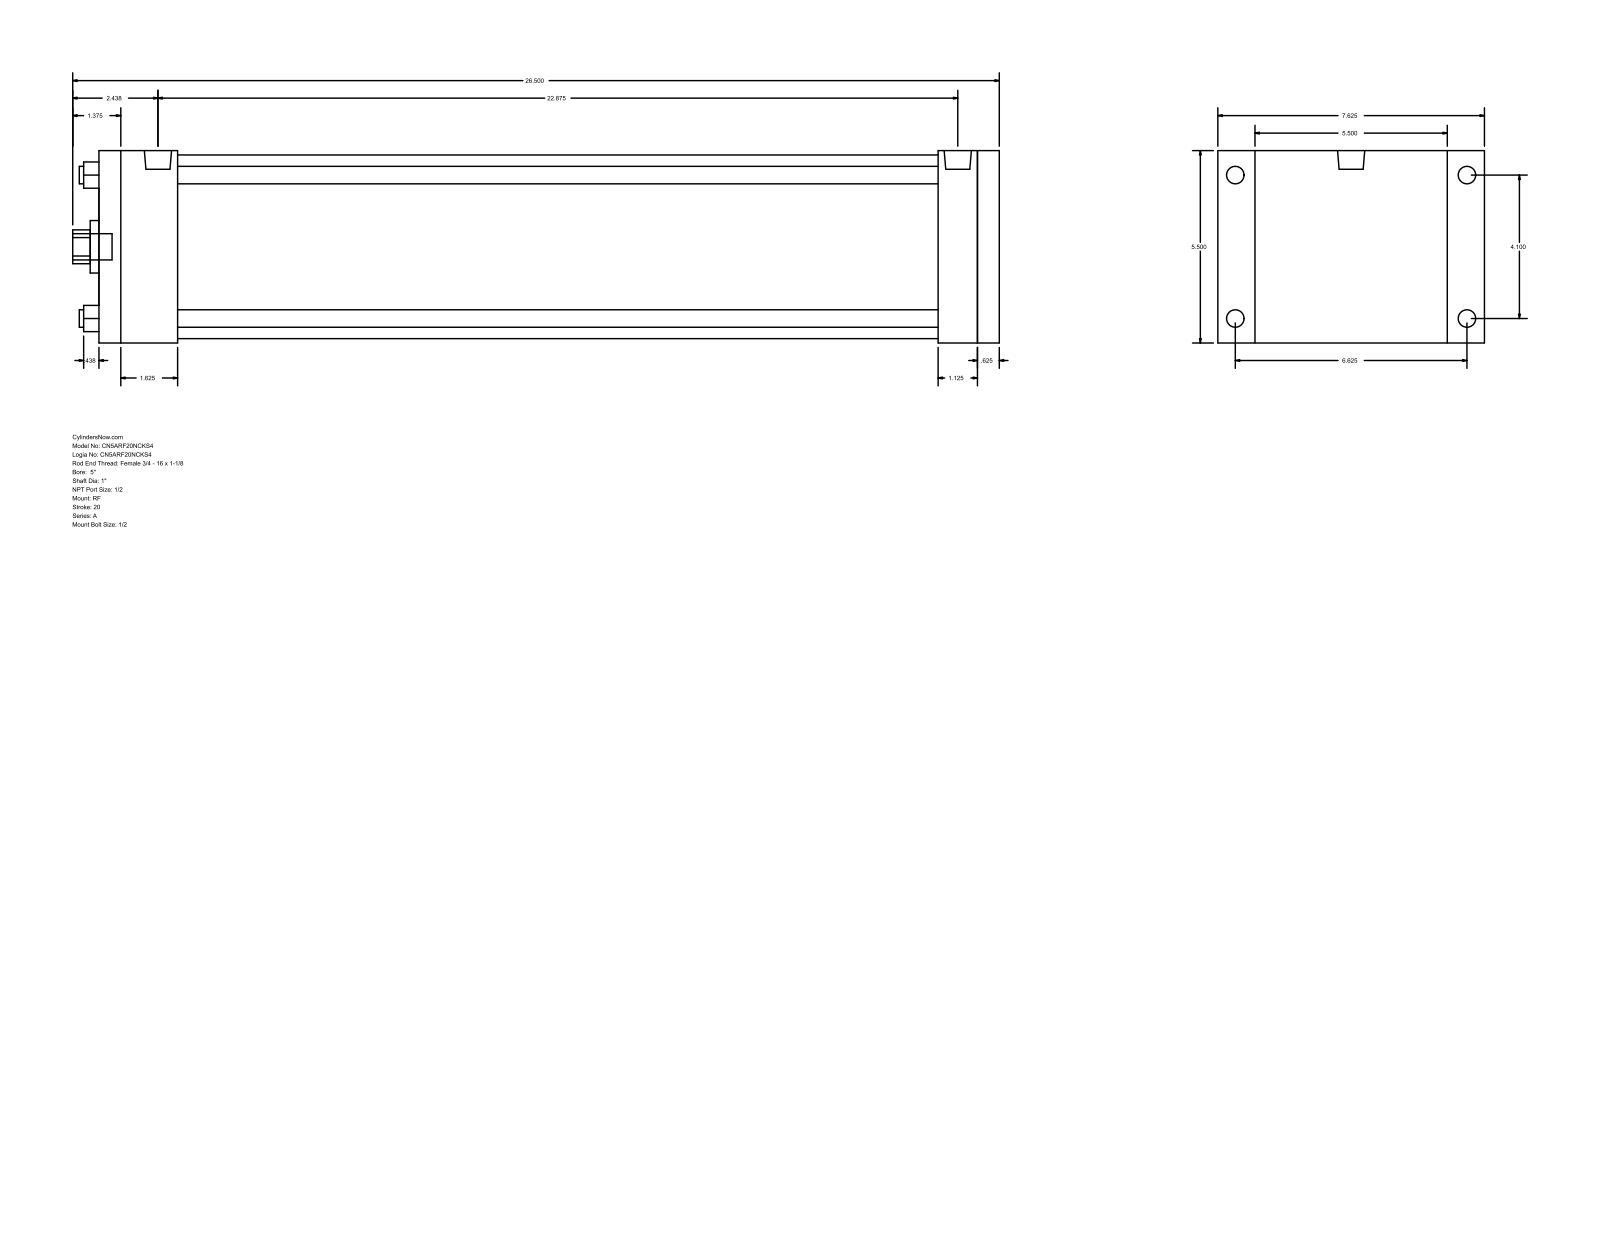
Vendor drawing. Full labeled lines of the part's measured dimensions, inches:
Part name (STEP PRODUCT): A_RF__0500_1
STEP written by: GSSL Pune (CONFIG_CONTROL_DESIGN)
Units: inches
Bodies: 0 solids, 92 faces (64 planar, 28 cylindrical, 0 other)
Overall size (bounding box): 26.5 × 7.625 × 5.5
Round holes (diameter × count): ⌀0.5 ×4, ⌀1 ×1, ⌀1.5 ×1, ⌀5.25 ×1
Round bosses / shafts (diameter × count): ⌀0.5 ×4, ⌀0.344 ×4, ⌀0.778 ×2, ⌀0.75 ×1
Partial cylindrical surfaces — rounded edges, fillets, slot ends (radius × count): R0.484 ×1
Main face-to-face distances: 5.5, 25.75, 0.625, 25.125, 2.25, 22.875, 23.5, 24, 21.75, 1.125
Hole centre spacings: 2.899, 4.1, 5.798
